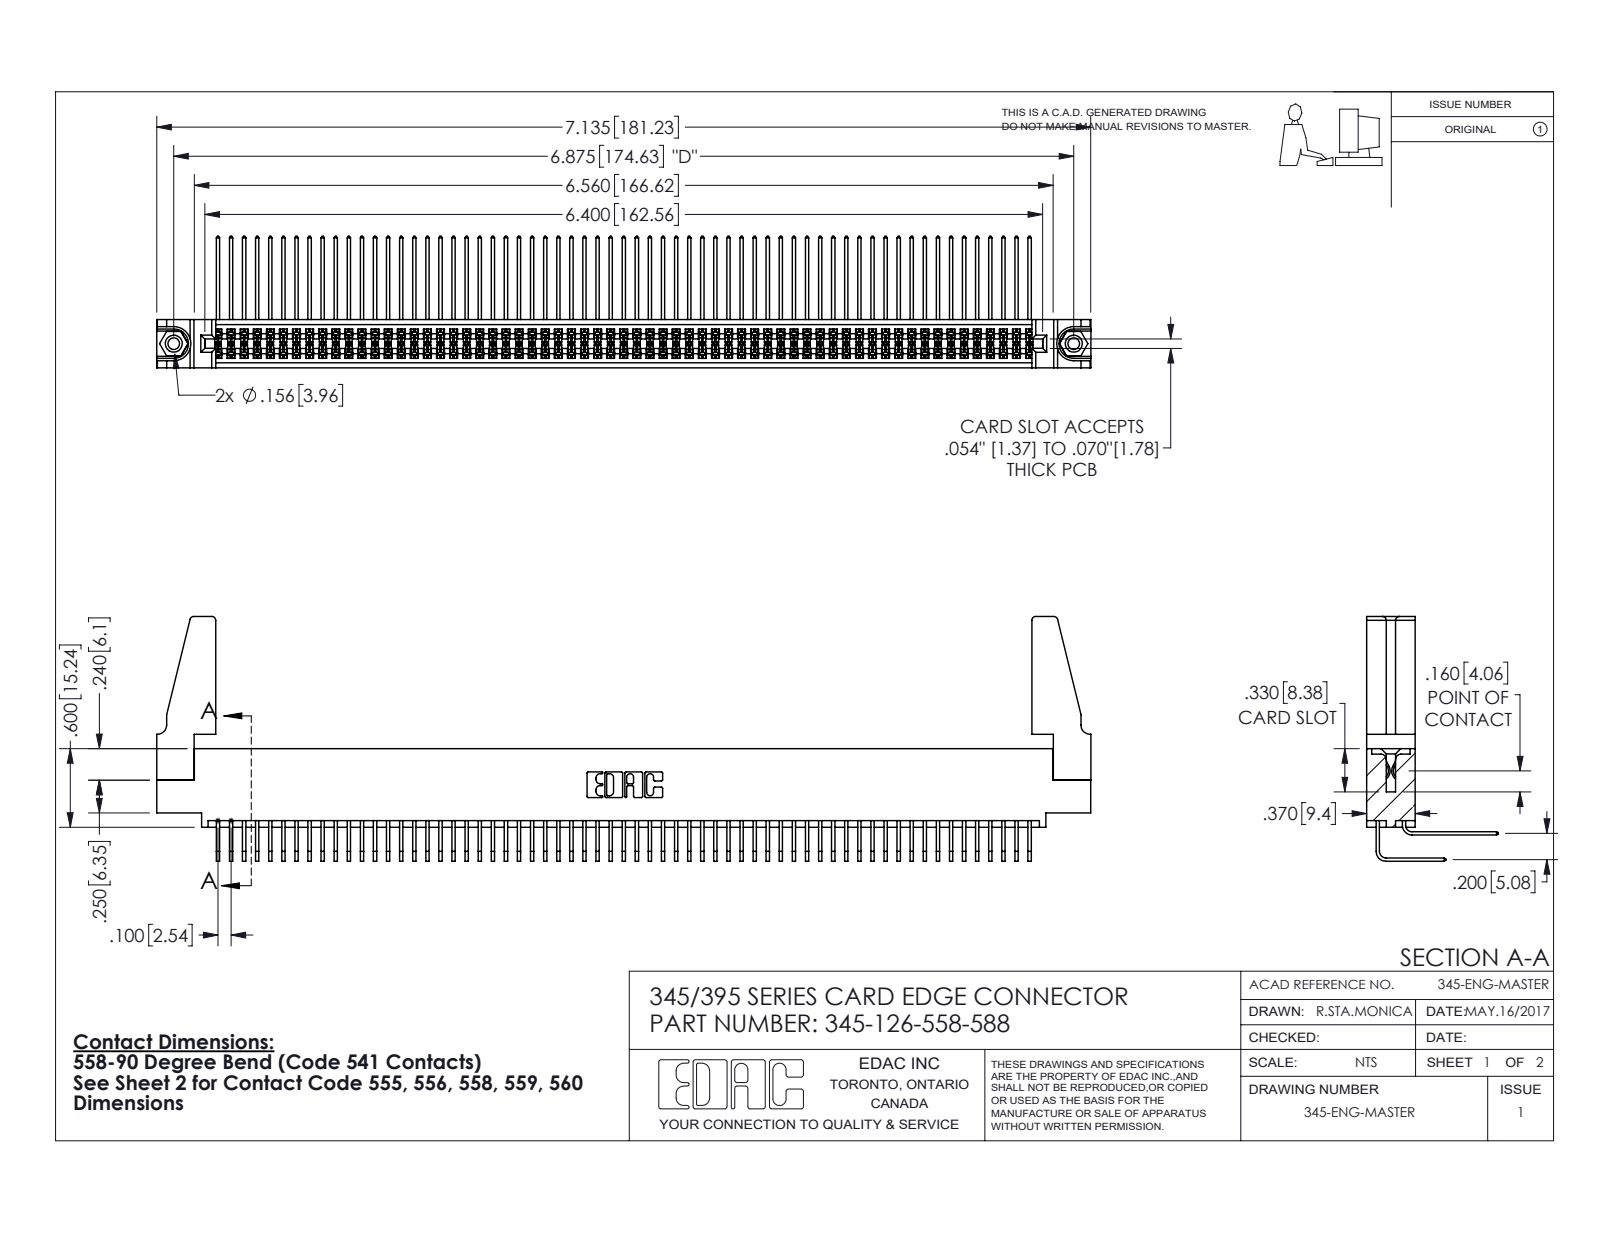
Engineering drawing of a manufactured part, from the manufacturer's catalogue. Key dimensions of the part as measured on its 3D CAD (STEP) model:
Part name (STEP PRODUCT): 345-292-001_558 Tail - 2; 345-126-558-588; 345 Part_0.110 Offset - 0.156 Dia-TH; 345-250-001_345-250-001-102 (+2 more)
STEP written by: SolidWorks 2016 (CONFIG_CONTROL_DESIGN)
Units: inches
Bodies: 131 solids, 6806 faces (4566 planar, 2224 cylindrical, 16 other)
Overall size (bounding box): 7.136 × 1.869 × 1.005
Volume: 1.325 in³ · Surface area: 53.2 in²
Round holes (diameter × count): ⌀0.089 ×2, ⌀0.125 ×2, ⌀0.156 ×2, ⌀0.064 ×1
Round bosses / shafts (diameter × count): ⌀0.155 ×2
Partial cylindrical surfaces — rounded edges, fillets, slot ends (radius × count): R0.006 ×252, R0.01 ×22, R0.03 ×8, R0.007 ×6, R0.031 ×6, R0.026 ×3, R0.014 ×2, R0.019 ×2
Main face-to-face distances: 0.072, 0.298, 0.2, 0.37, 0.098, 0.272, 0.025, 0.225, 0.025, 0.175
Hole centre spacings: 0.27, 6.639, 6.875
